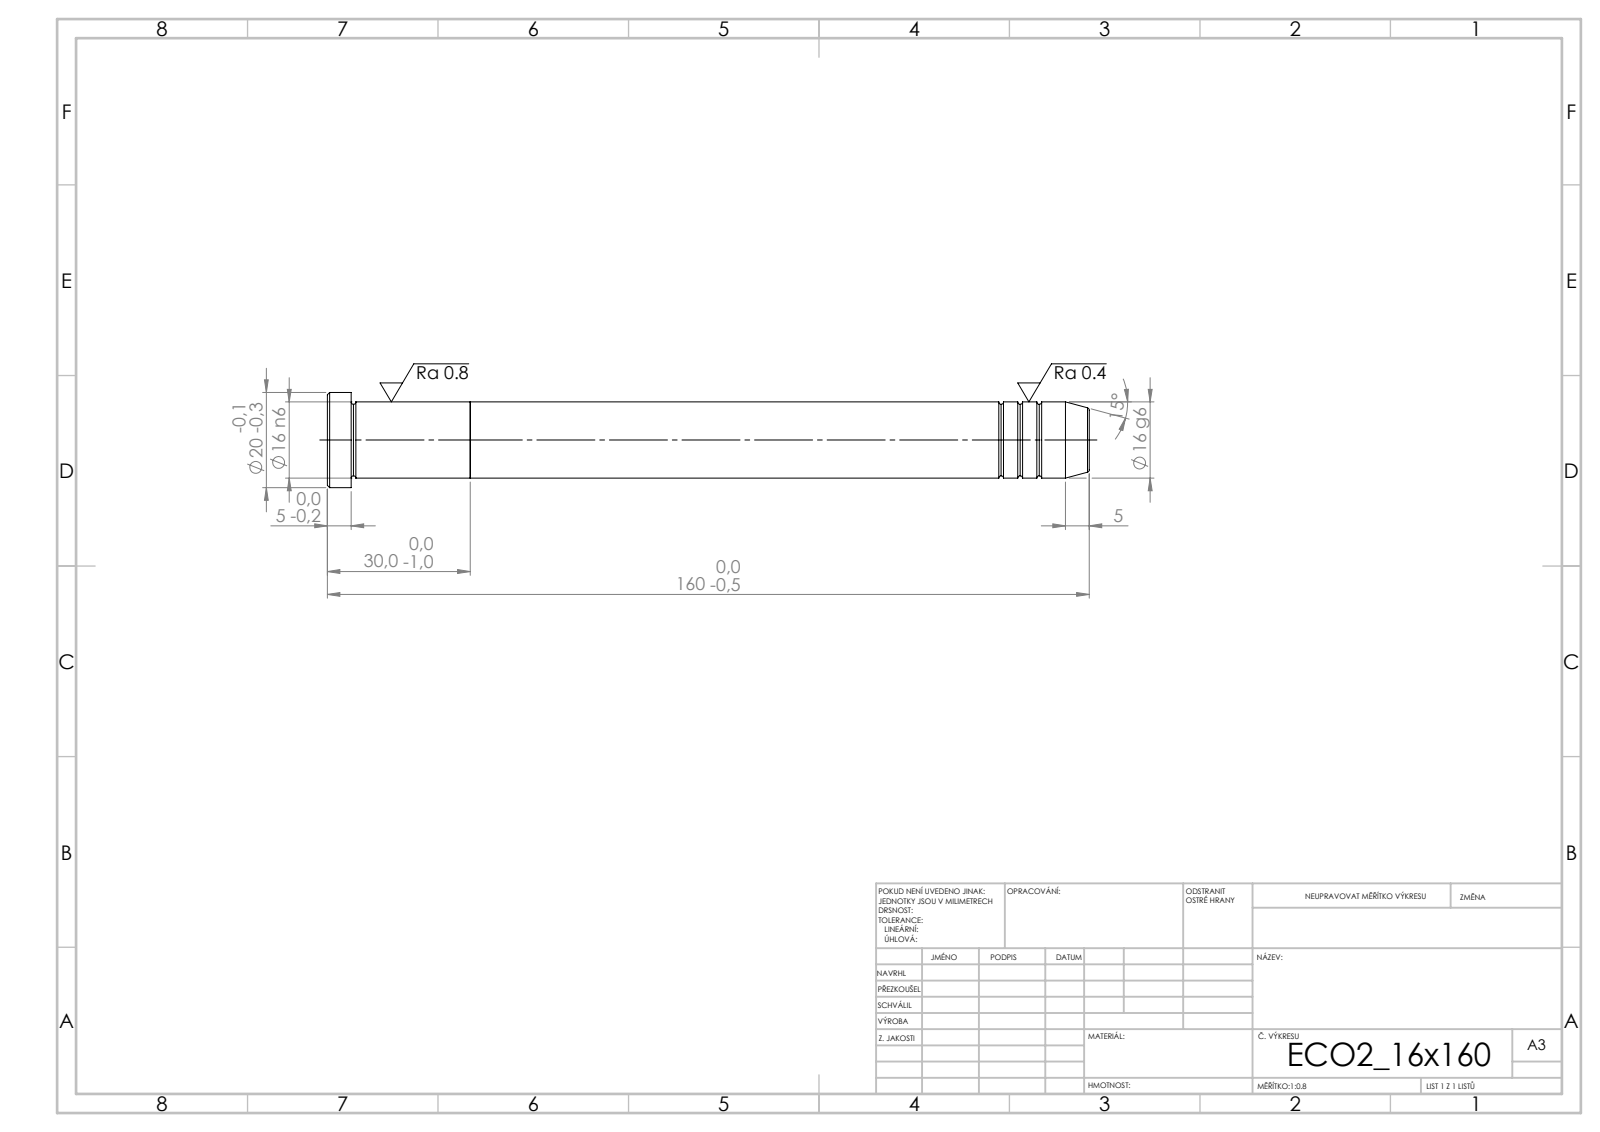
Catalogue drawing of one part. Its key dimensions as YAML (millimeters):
step_written_by: "SolidWorks 2019 (CONFIG_CONTROL_DESIGN)"
units: millimeters
bodies: {solids: 2, faces: 39, planar: 5, cylindrical: 12, other: 22}
overall_size: [160, 20, 20]
volume: 32491
surface_area: 9140
round_bosses_or_shafts:
  - {diameter: 20, count: 1}
  - {diameter: 16, count: 1}
face_to_face_distances: [30, 130, 160, 155, 25, 5]
